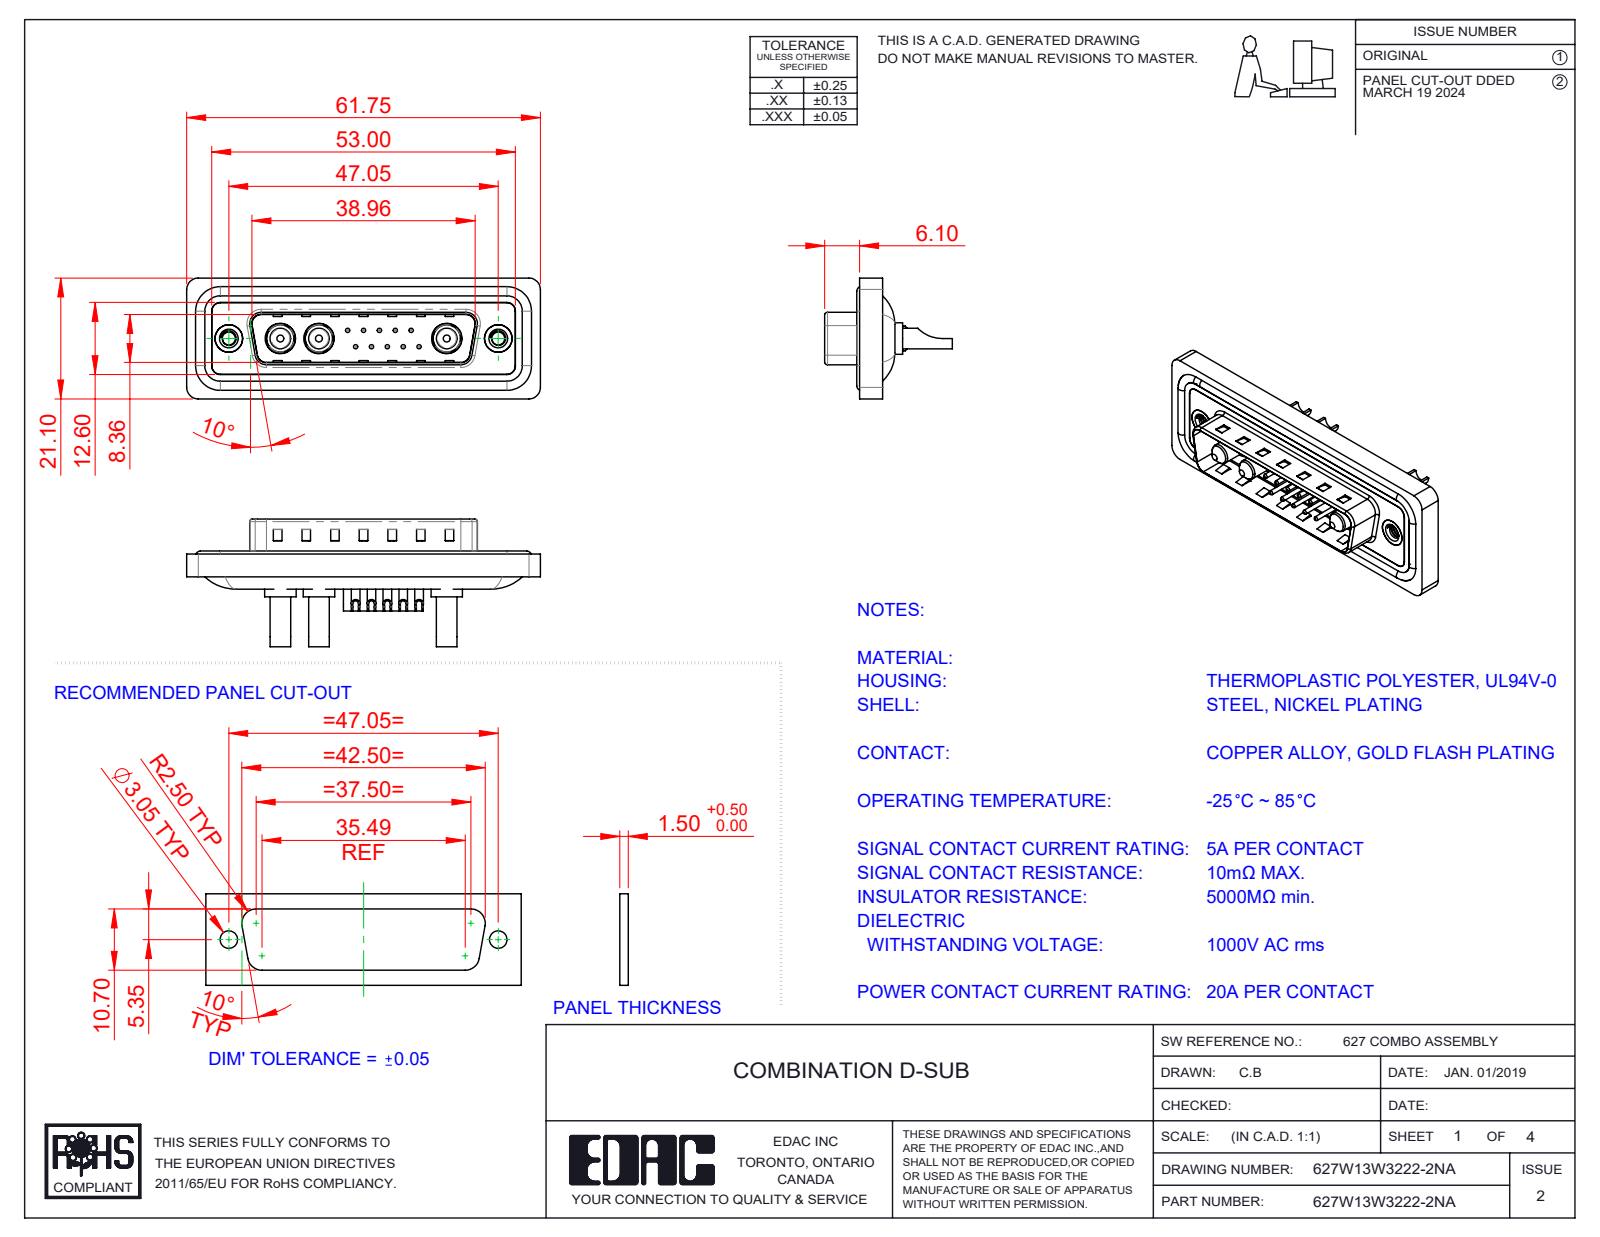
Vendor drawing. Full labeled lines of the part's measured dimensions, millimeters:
Part name (STEP PRODUCT): Power Pin_20A SC; 627Combo Contact Row 2_22; 627Combo Contact Row 1_22; 627Combo Shell Rear_25 Contacts (+5 more)
STEP written by: SolidWorks 2023 (CONFIG_CONTROL_DESIGN)
Units: millimetres
Bodies: 23 solids, 989 faces (338 planar, 416 cylindrical, 235 other)
Overall size (bounding box): 61.75 × 22.3 × 21.1
Volume: 7 391 mm³ · Surface area: 12 199 mm²
Round holes (diameter × count): ⌀0.75 ×10, ⌀1 ×10, ⌀1.6 ×10, ⌀2 ×10, ⌀2.7 ×3, ⌀4.85 ×3, ⌀5.3 ×3, ⌀2.26 ×2, ⌀4 ×2, ⌀4.8 ×2, ⌀5 ×2
Round bosses / shafts (diameter × count): ⌀1.5 ×10, ⌀1.6 ×4, ⌀5.5 ×3, ⌀5.2 ×3, ⌀4.75 ×3, ⌀3.75 ×3, ⌀3.6 ×3, ⌀4.9 ×2
Partial cylindrical surfaces — rounded edges, fillets, slot ends (radius × count): R1.5 ×22, R2 ×18, R0.5 ×8, R1.6 ×8, R1 ×6, R0.25 ×4, R0.6 ×4, R0.65 ×4
Main face-to-face distances: 0.4, 1.5, 1.1, 1.6, 0.5, 3.1, 2.9, 0.82, 9.58, 4.1
Hole centre spacings: 3.16, 2.77, 5.04, 5.54, 7.49, 5.03, 8.31, 10.11
